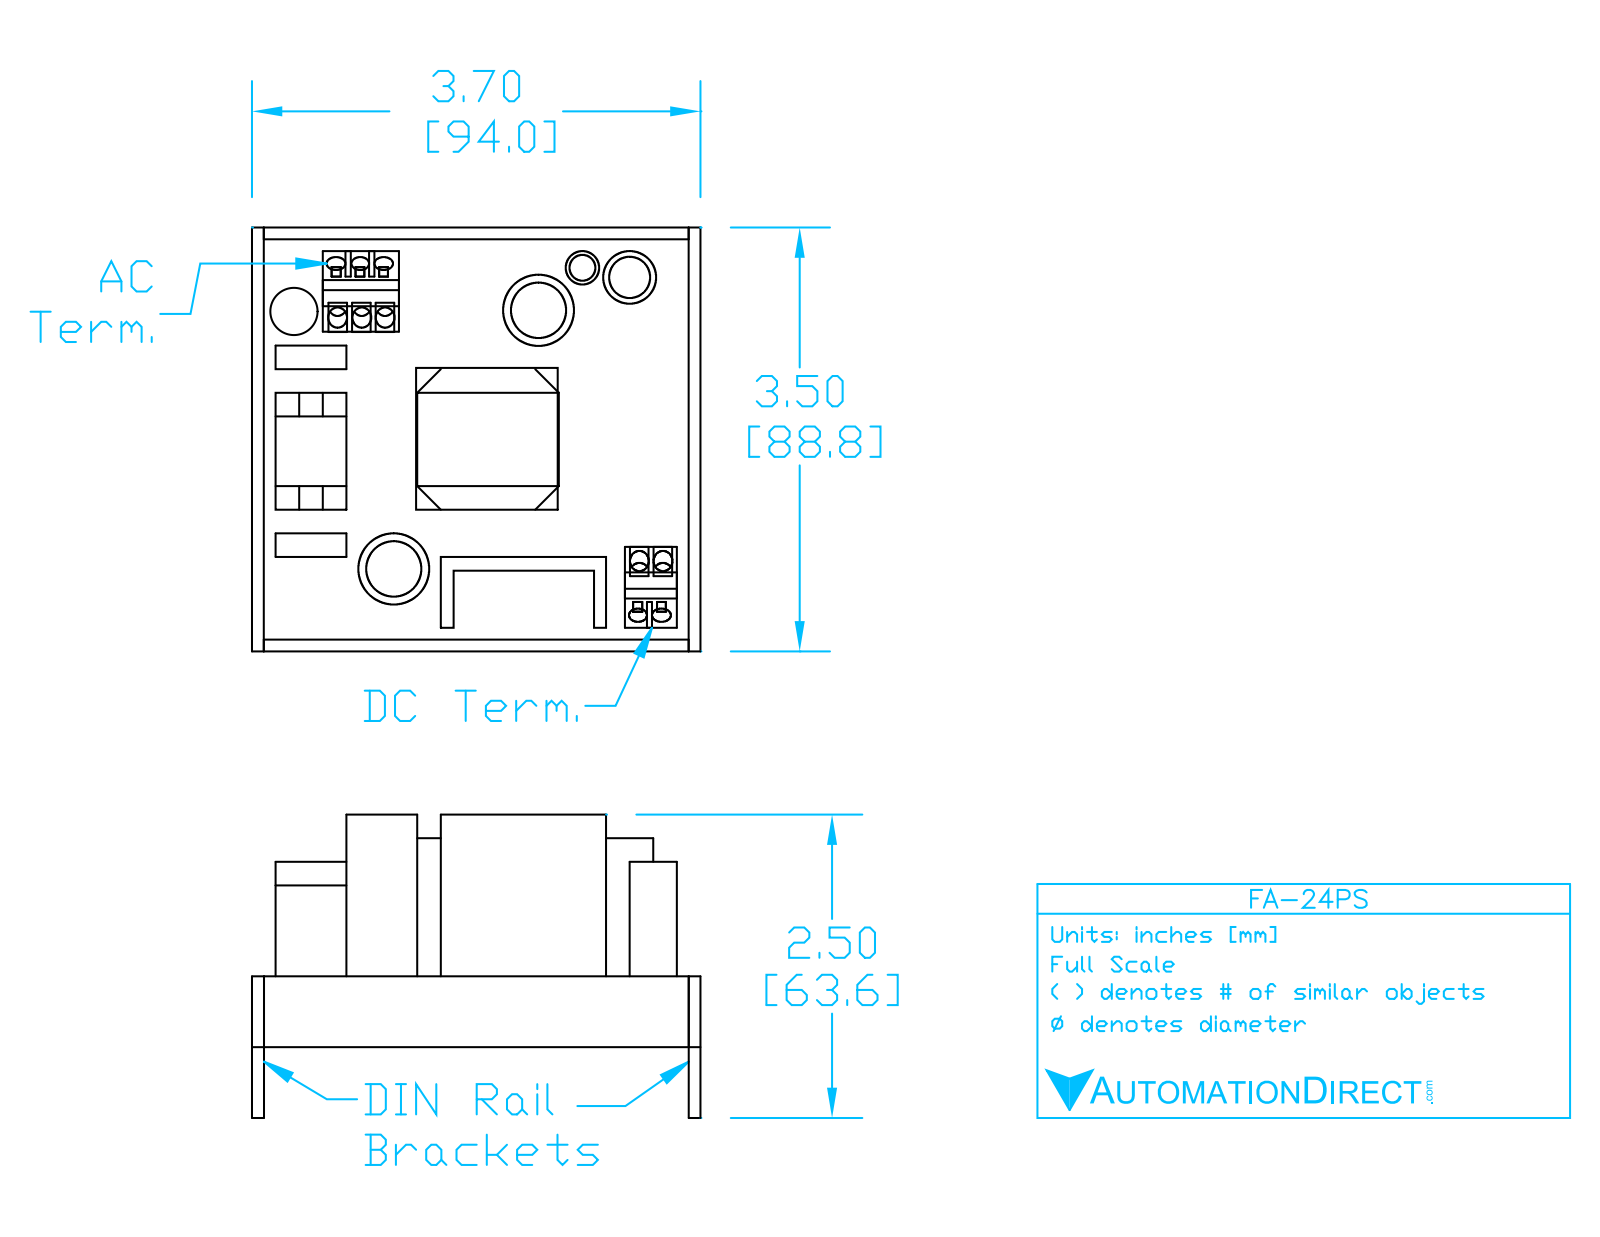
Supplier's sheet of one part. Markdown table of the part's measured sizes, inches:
| quantity | value |
| --- | --- |
| part name | FA-24PS |
| STEP written by | SolidWorks 2011 (CONFIG_CONTROL_DESIGN) |
| units | inches |
| bodies | 1 solid, 800 faces (513 planar, 217 cylindrical, 70 other) |
| overall size | 3.556 × 3.42 × 2.5 |
| volume | 10.14 in³ |
| surface area | 71.24 in² |
| round holes (diameter × count) | 0.12 × 5, 0.225 × 2 |
| round bosses / shafts (diameter × count) | 0.046 × 9, 0.134 × 3, 0.205 × 2, 0.59 × 1, 0.411 × 1, 0.345 × 1, 0.319 × 1, 0.235 × 1 |
| partial cylindrical surfaces (radius × count) | 0.015 × 41, 0.03 × 26, 0.06 × 20, 0.05 × 4, 0.069 × 2, 0.073 × 2, 0.1 × 2, 0.13 × 2 |
| main face-to-face distances | 0.628, 3.5, 0.03, 0.658, 0.09, 0.452, 1.08, 1.11, 0.1, 0.19 |
| hole center spacings | 0.2, 0.4, 2.85 |
